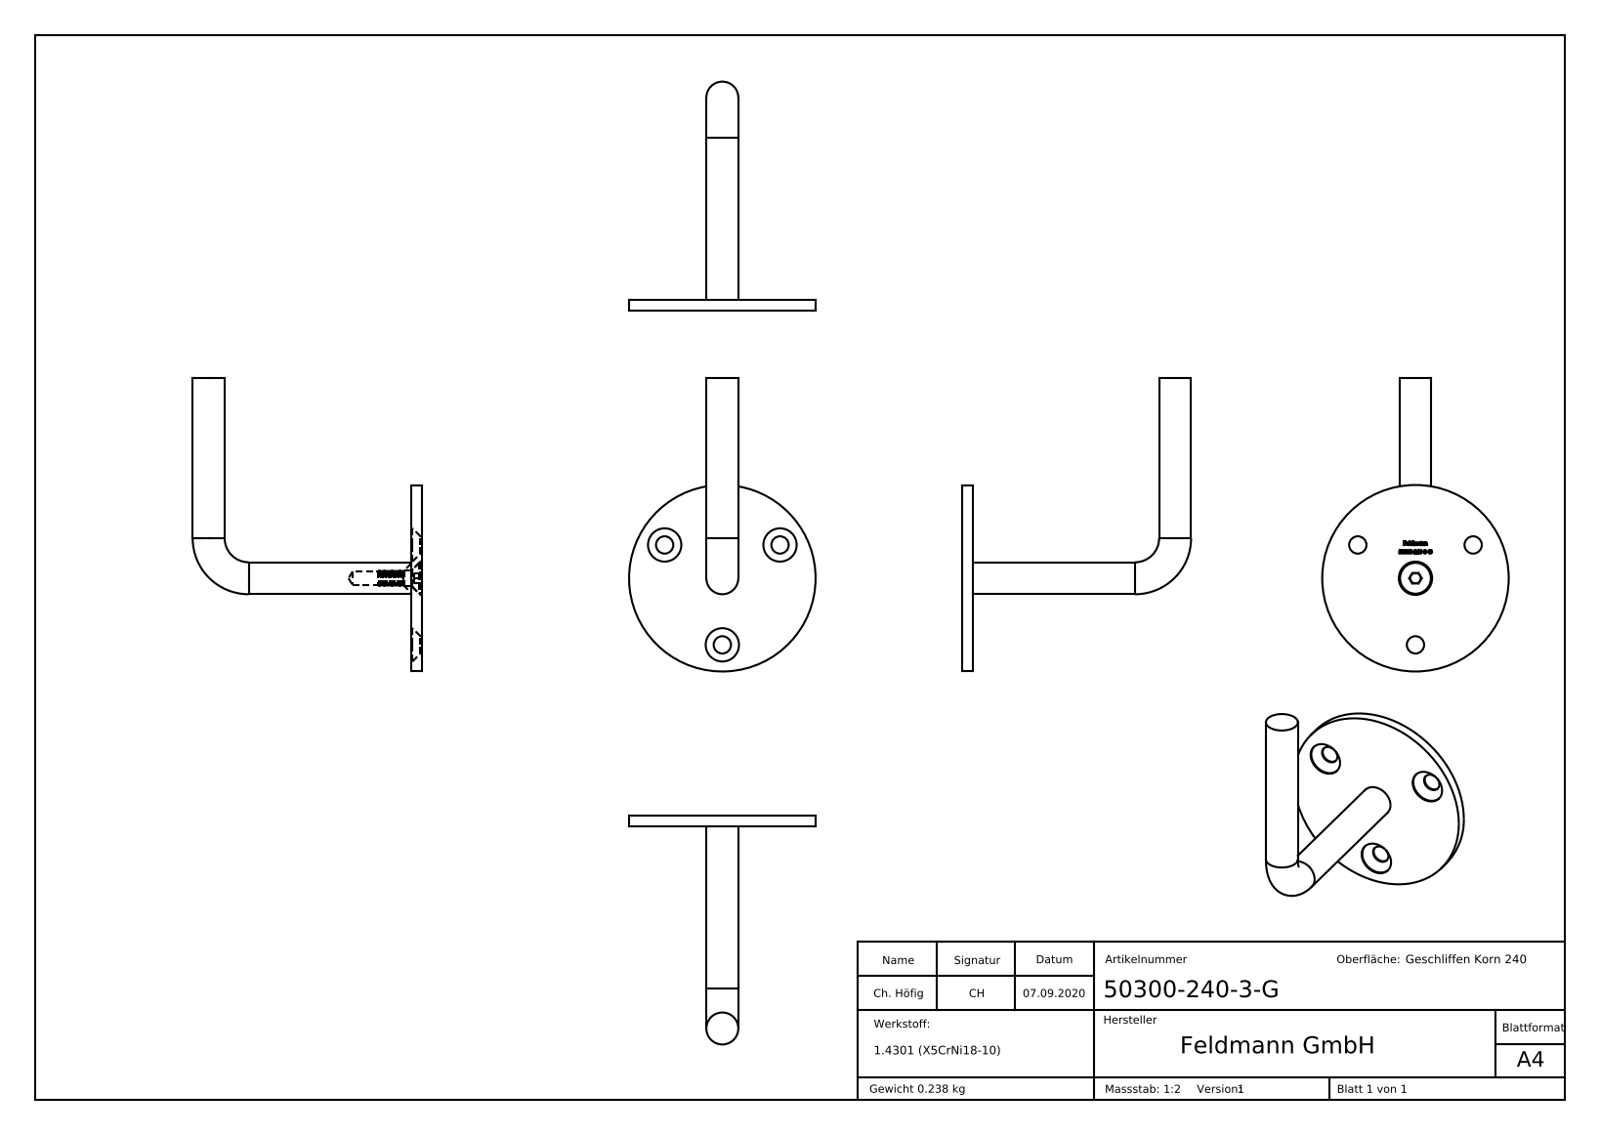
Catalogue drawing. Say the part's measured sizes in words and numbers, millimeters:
The part is named "50300-240-3-G Teil2; 50300-240-3-G Teil1; 50300-240-3-G Teil2_50300-240-3-G Teil2; socket countersunk head screw_din (+3 more)". Its 3-D file was written by "SolidWorks 2018 (CONFIG_CONTROL_DESIGN)". It is 3 solids with 338 faces: 148 planar, 24 cylindrical and 166 other. Overall it measures 110 by 86 by 70 millimeters. Its volume is 30 518 cubic millimeters and its surface area 15 215 square millimeters. Round holes: 4 of diameter 6.5, 4 of diameter 12.5, 1 of diameter 5. Round bosses or shafts: 2 of diameter 12, 1 of diameter 70, 1 of diameter 11.57, 1 of diameter 6. The main face-to-face distances are 4, 3.55, 0.45, 16.45, 16, 12.45, 4.02, 0.35, 3.9, 16.35. The hole center spacings are 25, 43.3.
